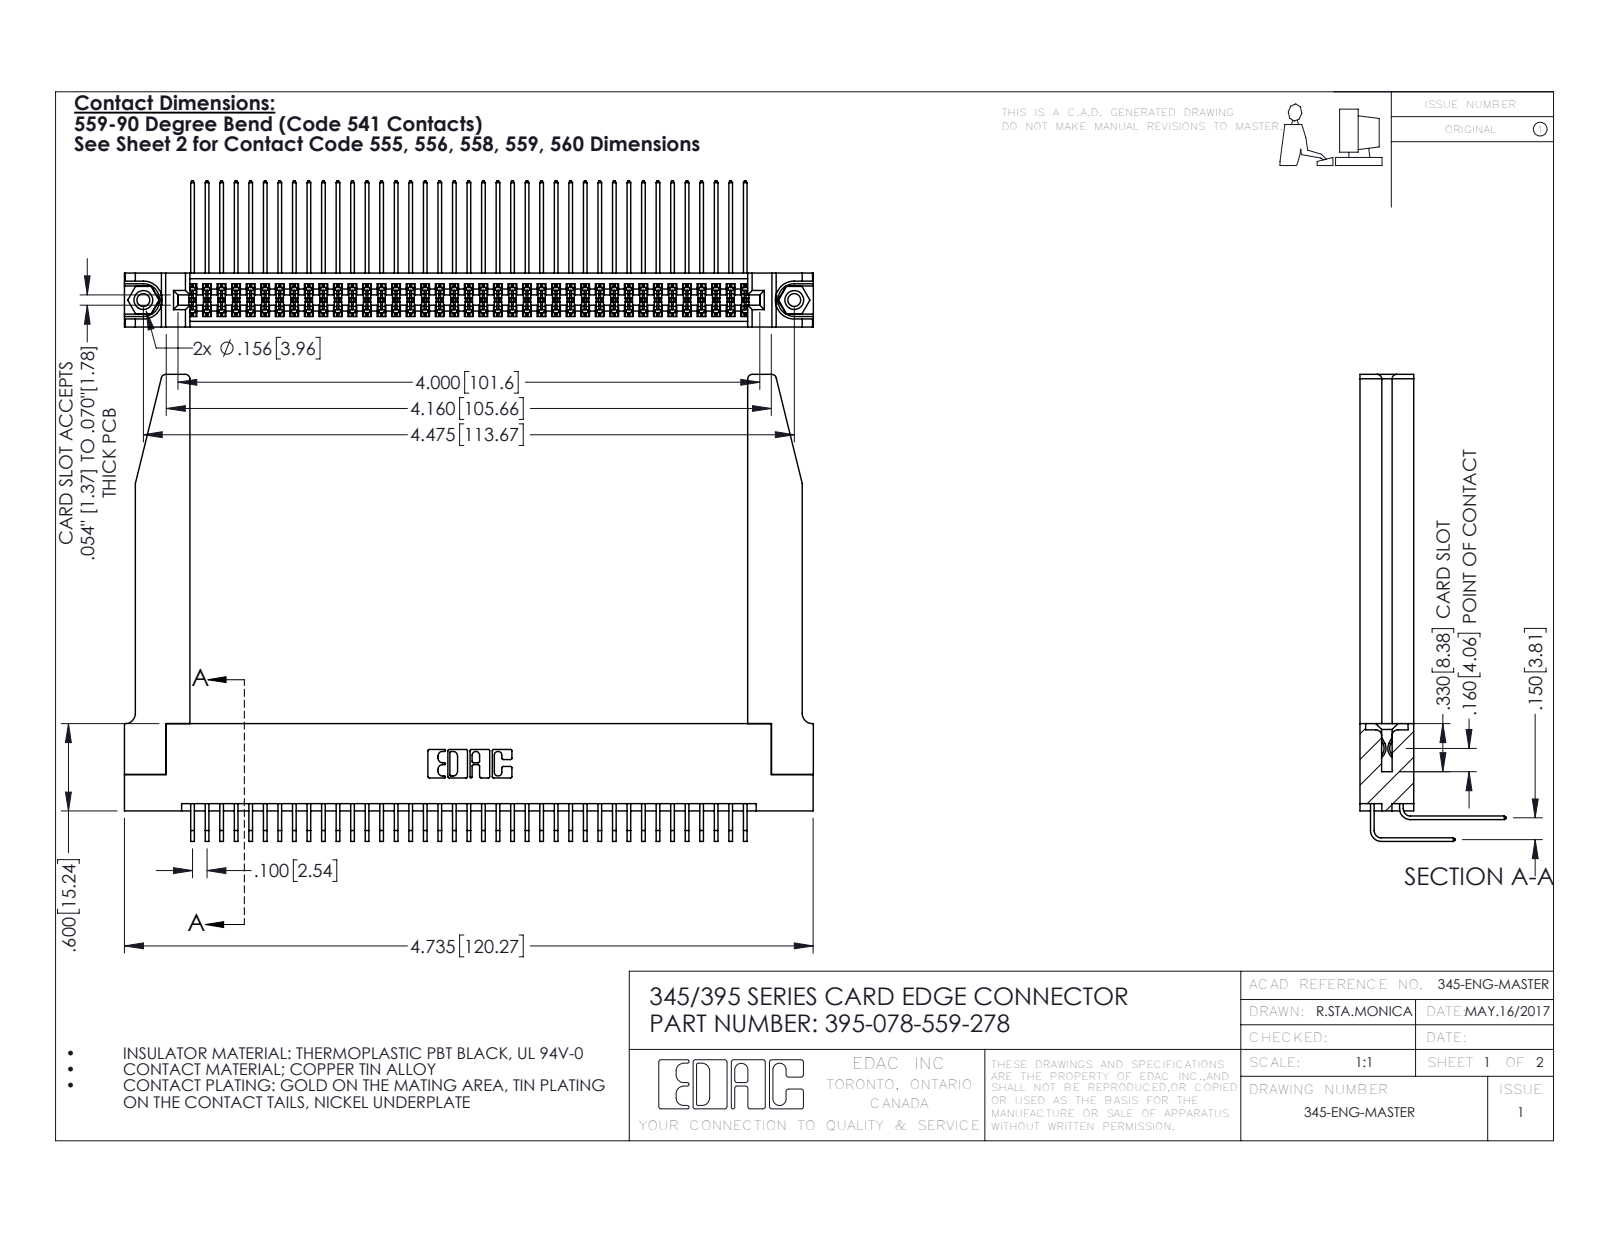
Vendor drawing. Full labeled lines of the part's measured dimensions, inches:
Part name (STEP PRODUCT): 345-292-001_559 Tail - 2; 345-250-001_345-250-001-102; 345-220-078_345-220-078; 395-078-559-278 (+2 more)
STEP written by: SolidWorks 2016 (CONFIG_CONTROL_DESIGN)
Units: inches
Bodies: 83 solids, 4416 faces (2952 planar, 1412 cylindrical, 52 other)
Overall size (bounding box): 4.736 × 3.209 × 1.005
Volume: 1.213 in³ · Surface area: 41.53 in²
Round holes (diameter × count): ⌀0.089 ×2, ⌀0.125 ×2, ⌀0.156 ×2, ⌀0.064 ×1
Round bosses / shafts (diameter × count): ⌀0.155 ×2
Partial cylindrical surfaces — rounded edges, fillets, slot ends (radius × count): R0.006 ×117, R0.01 ×22, R0.03 ×8, R0.007 ×6, R0.031 ×6, R0.026 ×3, R0.014 ×2, R0.019 ×2
Main face-to-face distances: 0.37, 0.072, 0.298, 0.2, 0.098, 0.272, 0.025, 0.225, 0.175, 0.15
Hole centre spacings: 0.27, 4.239, 4.475
